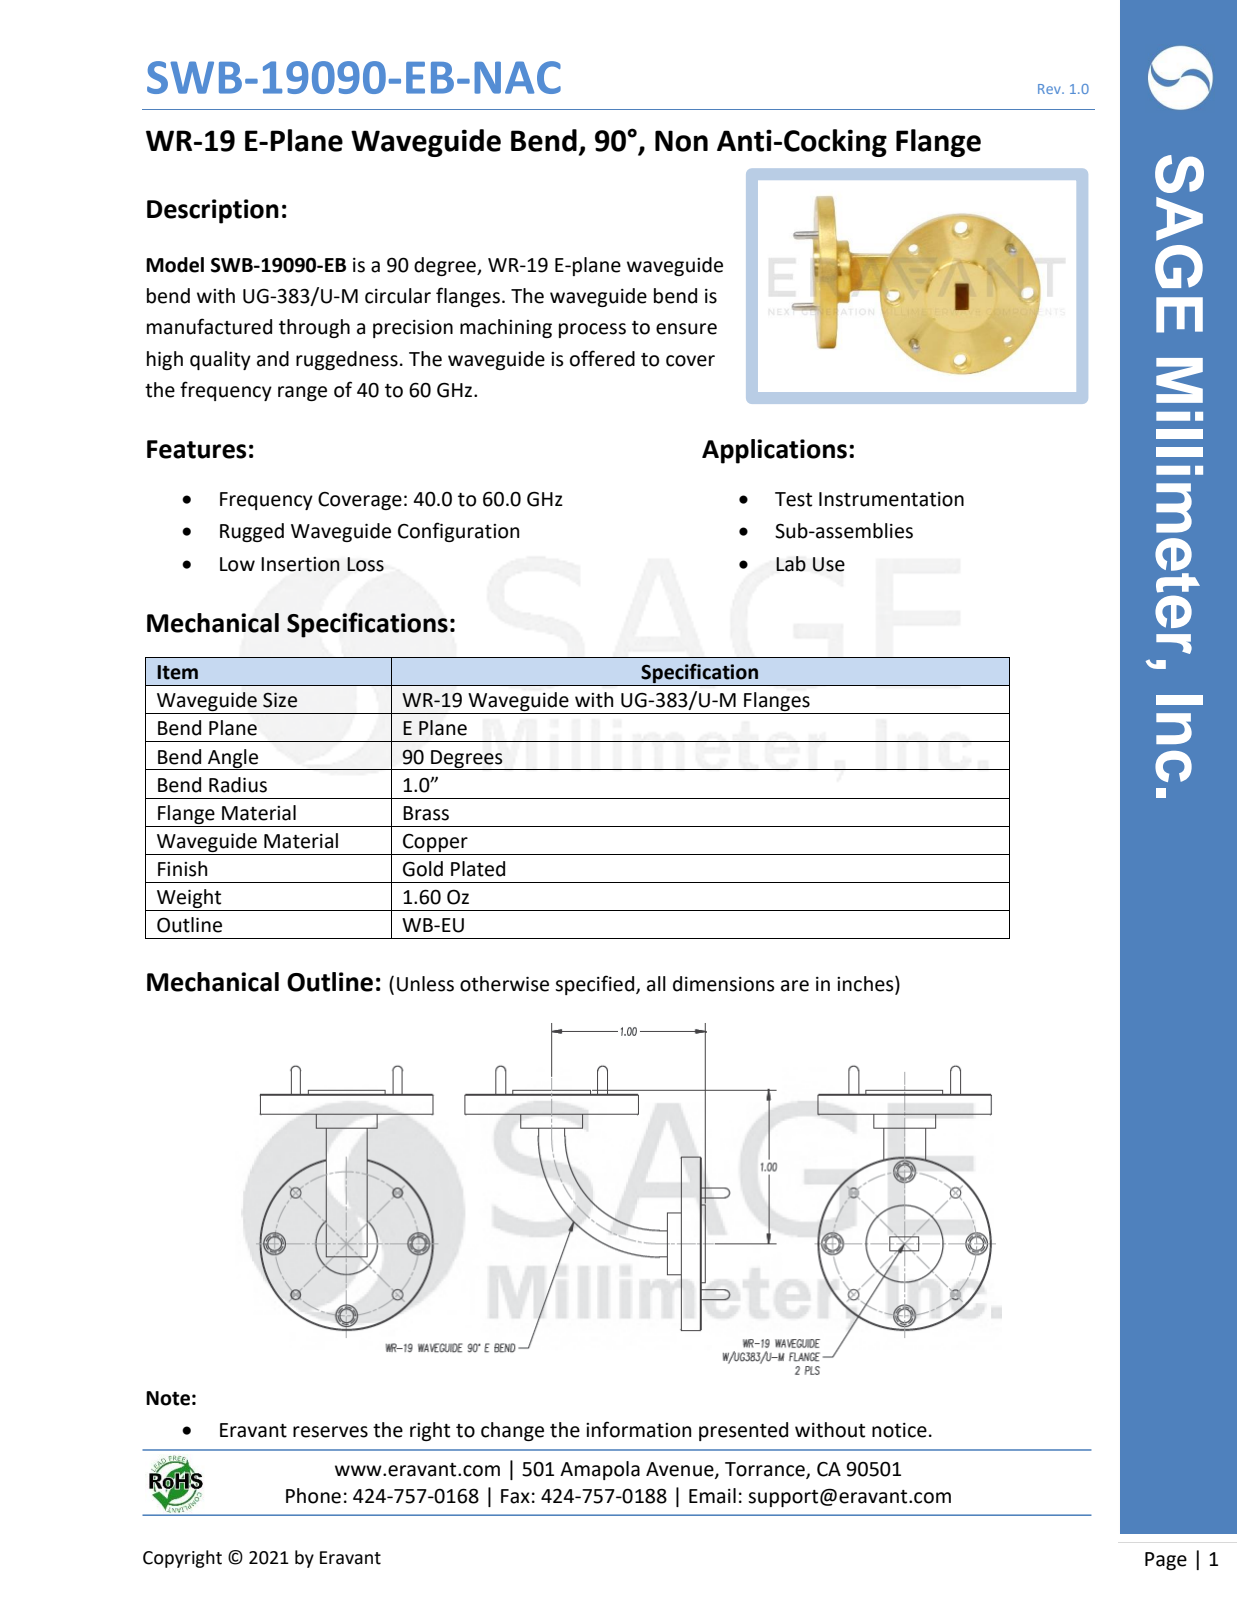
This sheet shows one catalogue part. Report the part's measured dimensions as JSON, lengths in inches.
{"part_name": "SWB-19090-EB", "step_written_by": "SolidWorks 2016 (CONFIG_CONTROL_DESIGN)", "units": "inches", "bodies": {"solids": 5, "faces": 150, "planar": 40, "cylindrical": 70, "other": 40}, "overall_size": [1.715, 1.715, 1.125], "volume_in3": 0.348, "surface_area_in2": 6.824, "round_holes": [[0.089, 8], [0.14, 8], [0.06, 4], [0.067, 4]], "round_bosses_or_shafts": [[0.063, 4], [1.125, 2], [0.5, 2], [0.475, 1], [0.35, 1]], "partial_cylinders_radius": [[0.413, 1], [0.587, 1]], "face_to_face_distances": [0.13, 0.13, 0.16, 0.268, 0.26, 0.1, 0.03, 0.03, 0.23, 0.913], "hole_center_spacings": [0.359, 0.866, 0.663, 0.937, 0.938, 0.663]}
